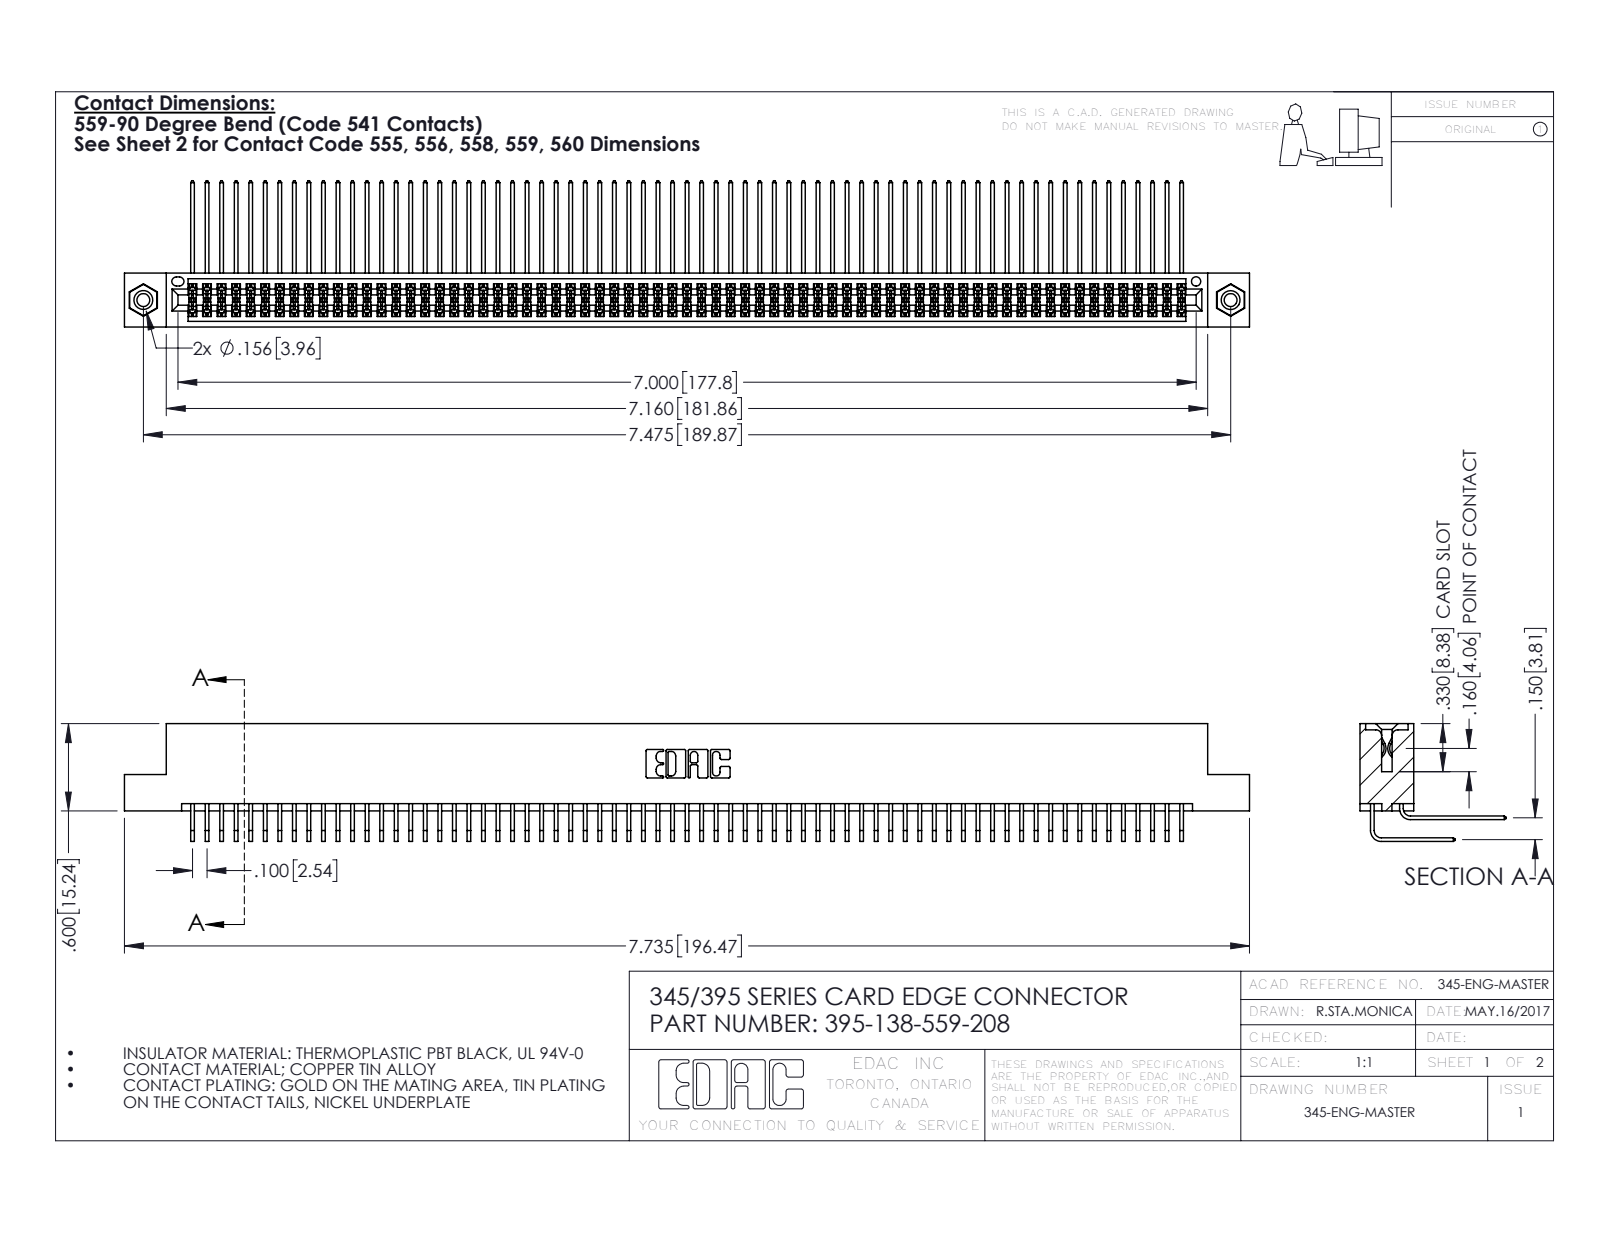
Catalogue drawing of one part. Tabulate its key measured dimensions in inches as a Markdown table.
| quantity | value |
| --- | --- |
| part name | 345-250-001_345-250-003-102; 395-138-559-208; 345-292-001_558 559 Tail - 1; 345 Part_Flush Mounting Lugs - 0.156 Dia-TI (+1 more) |
| STEP written by | SolidWorks 2016 (CONFIG_CONTROL_DESIGN) |
| units | inches |
| bodies | 141 solids, 7362 faces (4942 planar, 2404 cylindrical, 16 other) |
| overall size | 7.735 × 1.005 × 0.809 |
| volume | 1.228 in³ |
| surface area | 52.74 in² |
| round holes (diameter × count) | 0.089 × 2, 0.125 × 2, 0.156 × 2, 0.064 × 1 |
| round bosses / shafts (diameter × count) | 0.155 × 2 |
| partial cylindrical surfaces (radius × count) | 0.006 × 275, 0.01 × 22, 0.007 × 6, 0.031 × 6, 0.026 × 3, 0.014 × 2, 0.019 × 2, 0.022 × 2 |
| main face-to-face distances | 0.072, 0.298, 0.2, 0.37, 0.098, 0.272, 0.025, 0.225, 0.175, 0.15 |
| hole center spacings | 0.27, 7.239, 7.475 |
